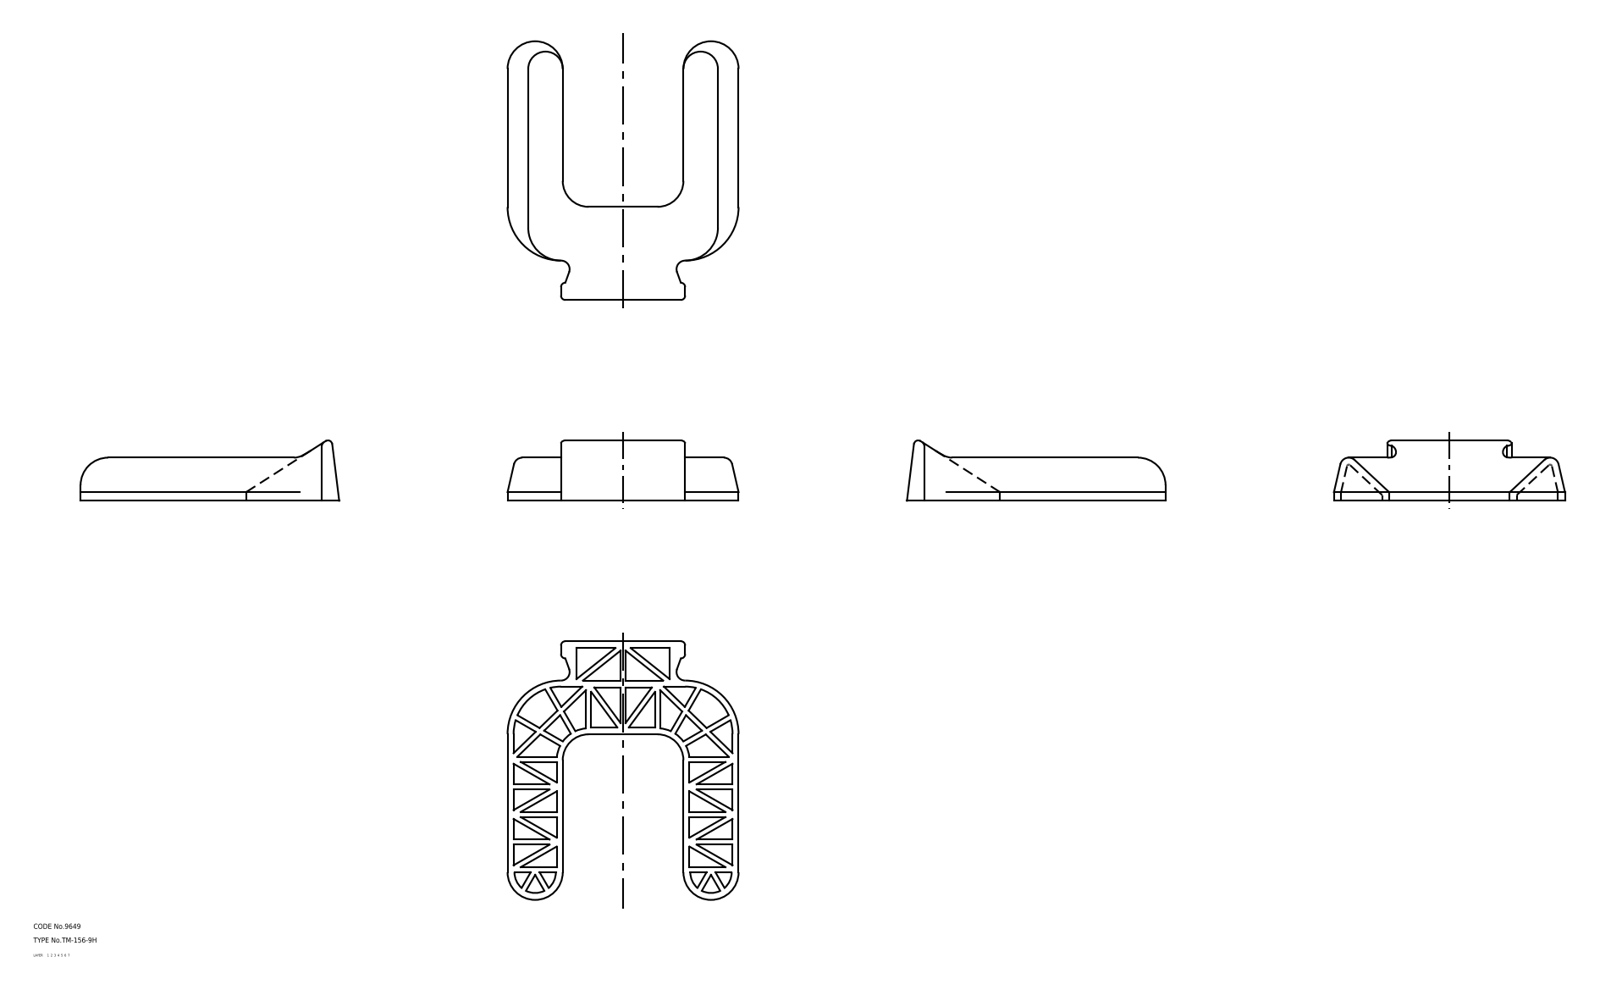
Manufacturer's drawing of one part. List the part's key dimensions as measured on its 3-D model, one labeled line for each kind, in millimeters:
Part name (STEP PRODUCT): 67125864
STEP written by: CADfix (AUTOMOTIVE_DESIGN)
Units: millimetres
Bodies: 1 solid, 358 faces (0 planar, 0 cylindrical, 358 other)
Overall size (bounding box): 150 × 134 × 35
Volume: 130 644 mm³ · Surface area: 67 808 mm²
